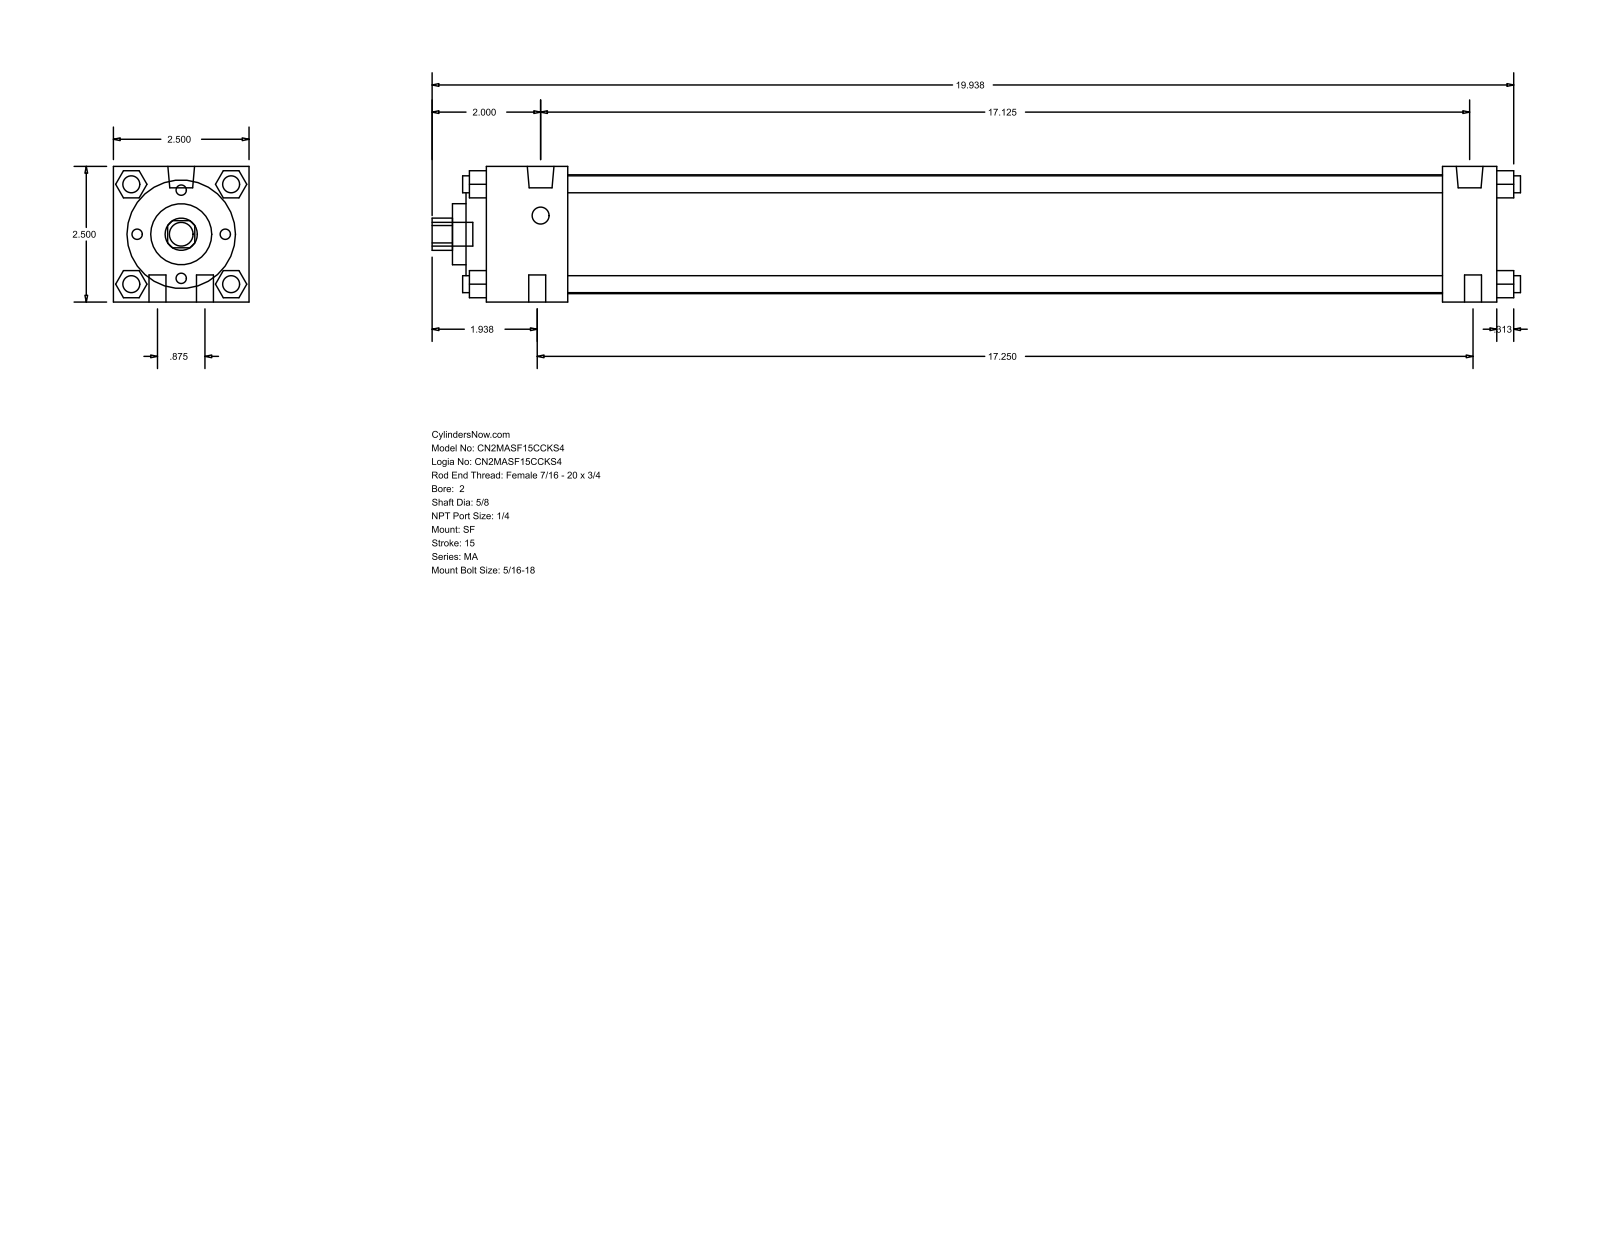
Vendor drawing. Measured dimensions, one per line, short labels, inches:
name: MA_SF__0200_0.625
written by: GSSL Pune (CONFIG_CONTROL_DESIGN)
unit: in
bodies: 0 solids, 126 faces (95 planar, 31 cylindrical, 0 other)
size: 20.063 × 2.5 × 2.5
holes: 1× ⌀0.625, 1× ⌀1.125, 1× ⌀2, 1× ⌀2.19
bosses: 10× ⌀0.313, 2× ⌀0.492, 1× ⌀0.437
rounds: 1× R0.297
face distances: 2.5, 0.5, 1.5, 0.375, 18.625, 17.625, 1, 16.125, 17.125, 1.875
